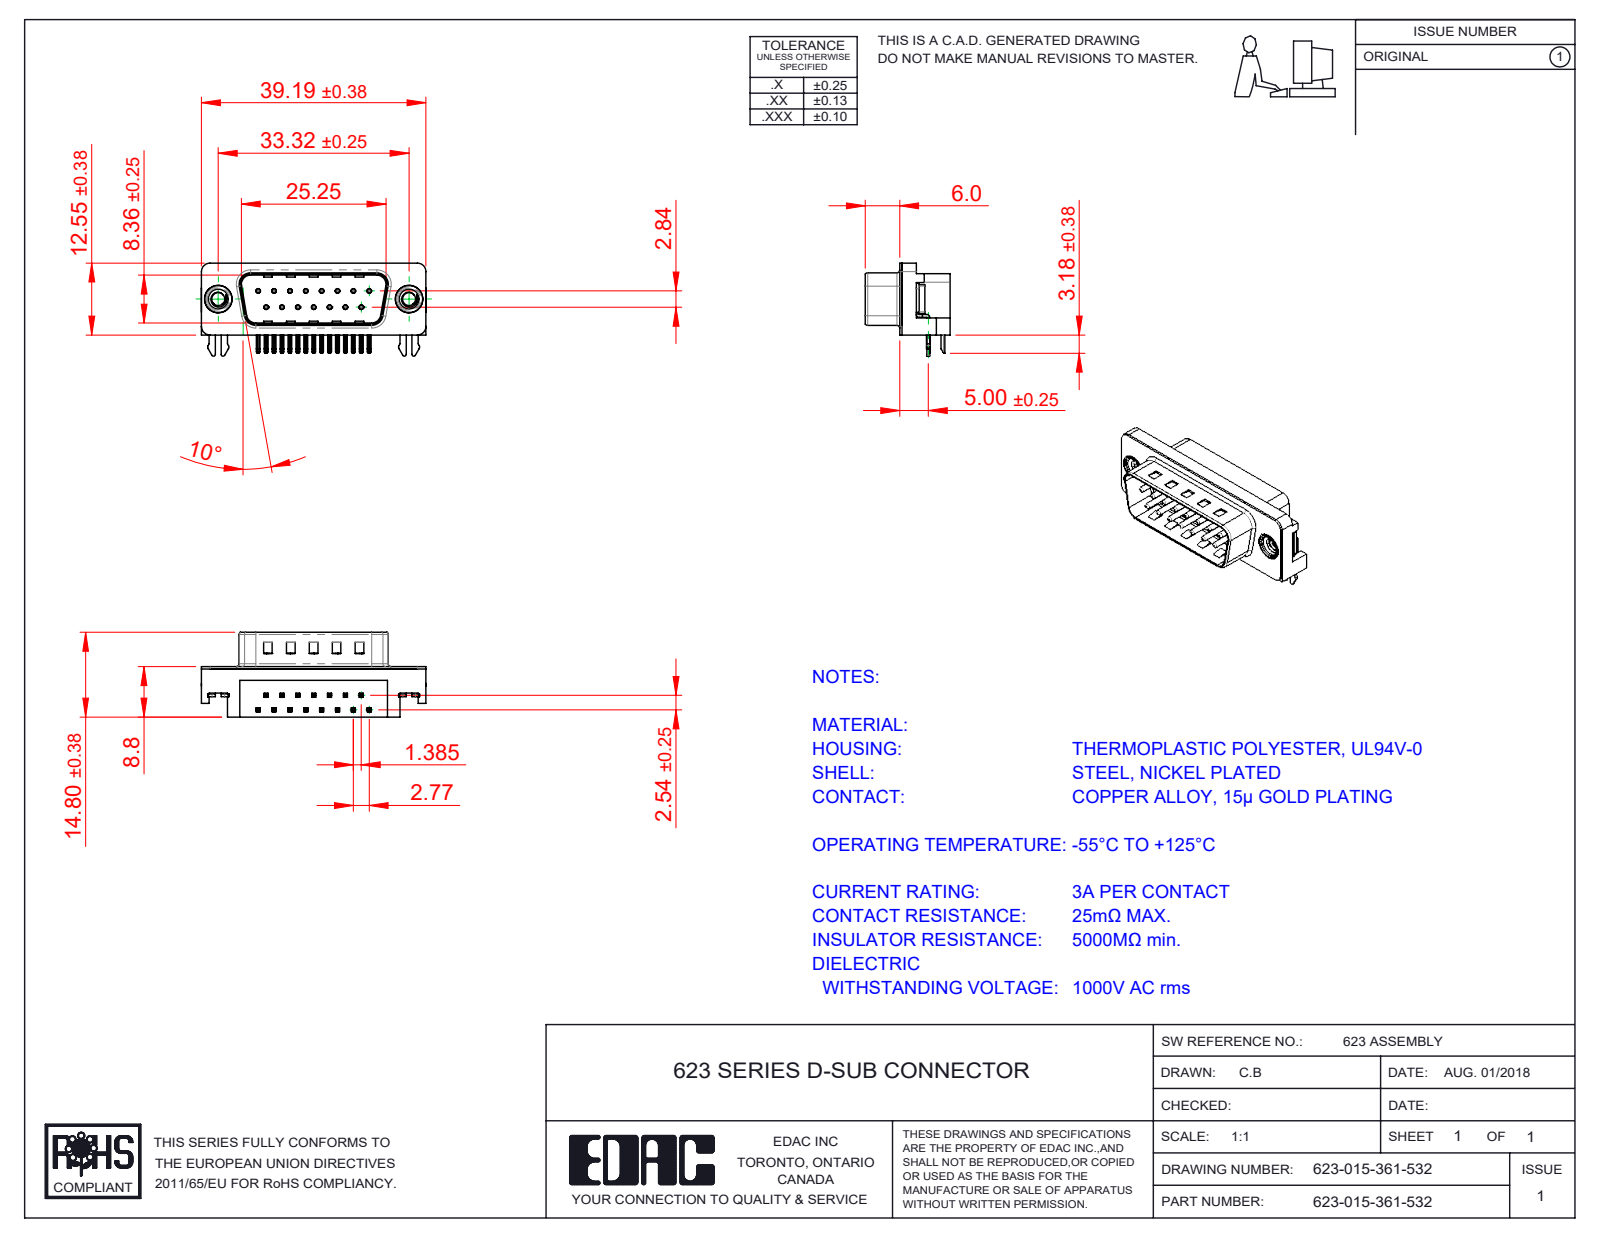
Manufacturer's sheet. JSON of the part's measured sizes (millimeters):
{"part_name": "623 2 Prong Board Lock; 623 Contact Bottom; 623 4-40 Threaded Rivet; 623 Housing_15 Socket (+3 more)", "step_written_by": "SolidWorks 2016 (CONFIG_CONTROL_DESIGN)", "units": "millimeters", "bodies": {"solids": 21, "faces": 1499, "planar": 921, "cylindrical": 439, "other": 139}, "overall_size": [39.22, 16.25, 14.8], "volume_mm3": 3328, "surface_area_mm2": 4947, "round_holes": [[0.35, 15], [0.8, 15], [2.26, 2], [4, 2], [4.8, 2], [5, 2]], "round_bosses_or_shafts": [[0.75, 15], [4.9, 2], [4.75, 2], [3.9, 2]], "partial_cylinders_radius": [[0.25, 68], [0.12, 30], [0.5, 14], [1, 8], [1.5, 6], [0.32, 4], [0.9, 4], [1.6, 4]], "face_to_face_distances": [0.4, 8.4, 2.1, 1.7, 10.46, 8.8, 10.86, 8.76, 5.9, 2.9], "hole_center_spacings": [3.16, 2.77, 5.54, 8.31, 11.08, 5.03, 5.04, 7.48]}
